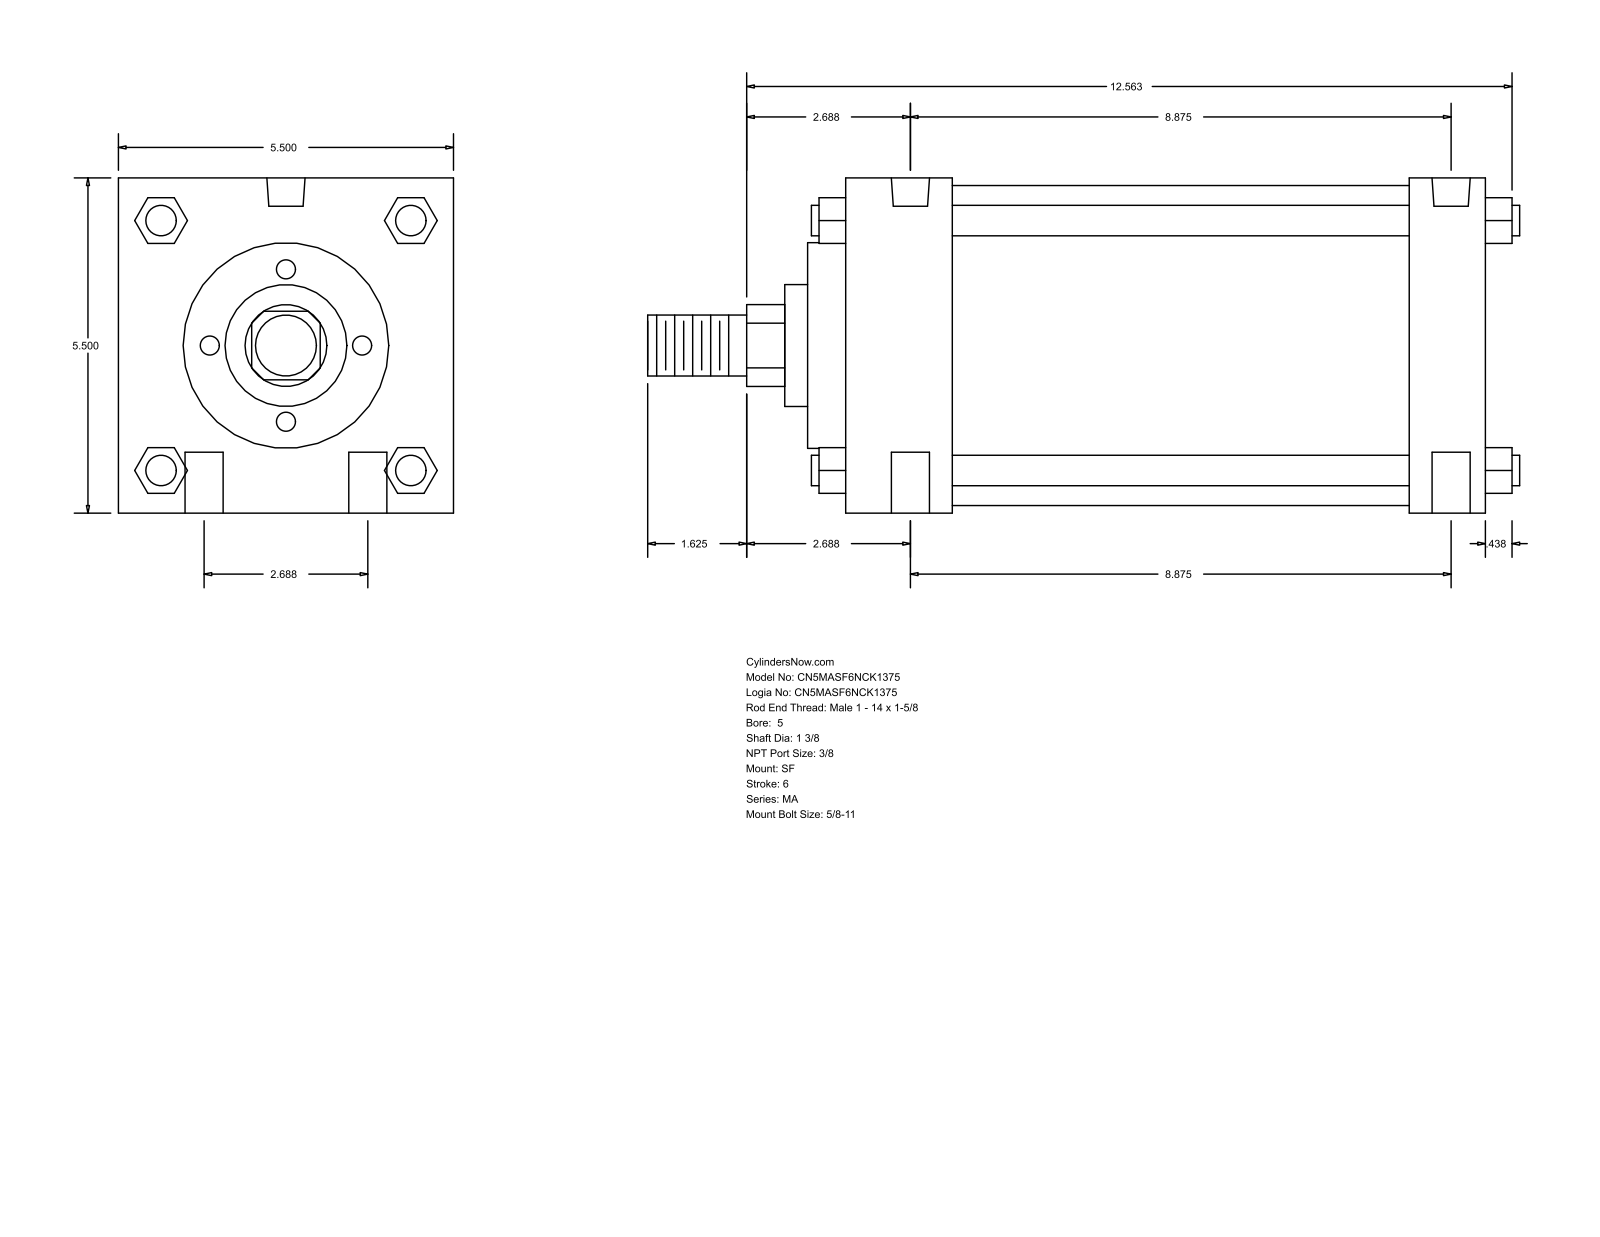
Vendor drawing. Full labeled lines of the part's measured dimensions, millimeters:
Part name (STEP PRODUCT): MA_SF__0500_1.375
STEP written by: GSSL Pune (CONFIG_CONTROL_DESIGN)
Units: millimetres
Bodies: 0 solids, 126 faces (95 planar, 31 cylindrical, 0 other)
Overall size (bounding box): 363.54 × 139.7 × 139.7
Round holes (diameter × count): ⌀15.88 ×4, ⌀11.11 ×2, ⌀15.93 ×2
Round bosses / shafts (diameter × count): ⌀12.7 ×4, ⌀133.35 ×1, ⌀85.72 ×1, ⌀50.8 ×1, ⌀34.92 ×1, ⌀25.4 ×1
Partial cylindrical surfaces — rounded edges, fillets, slot ends (radius × count): R17.06 ×1
Main face-to-face distances: 139.7, 266.71, 44.45, 234.96, 190.51, 222.26, 31.75, 15.87, 60.32, 250.83
Hole centre spacings: 34.13, 228, 225.43, 68.26, 235.54, 215.9
